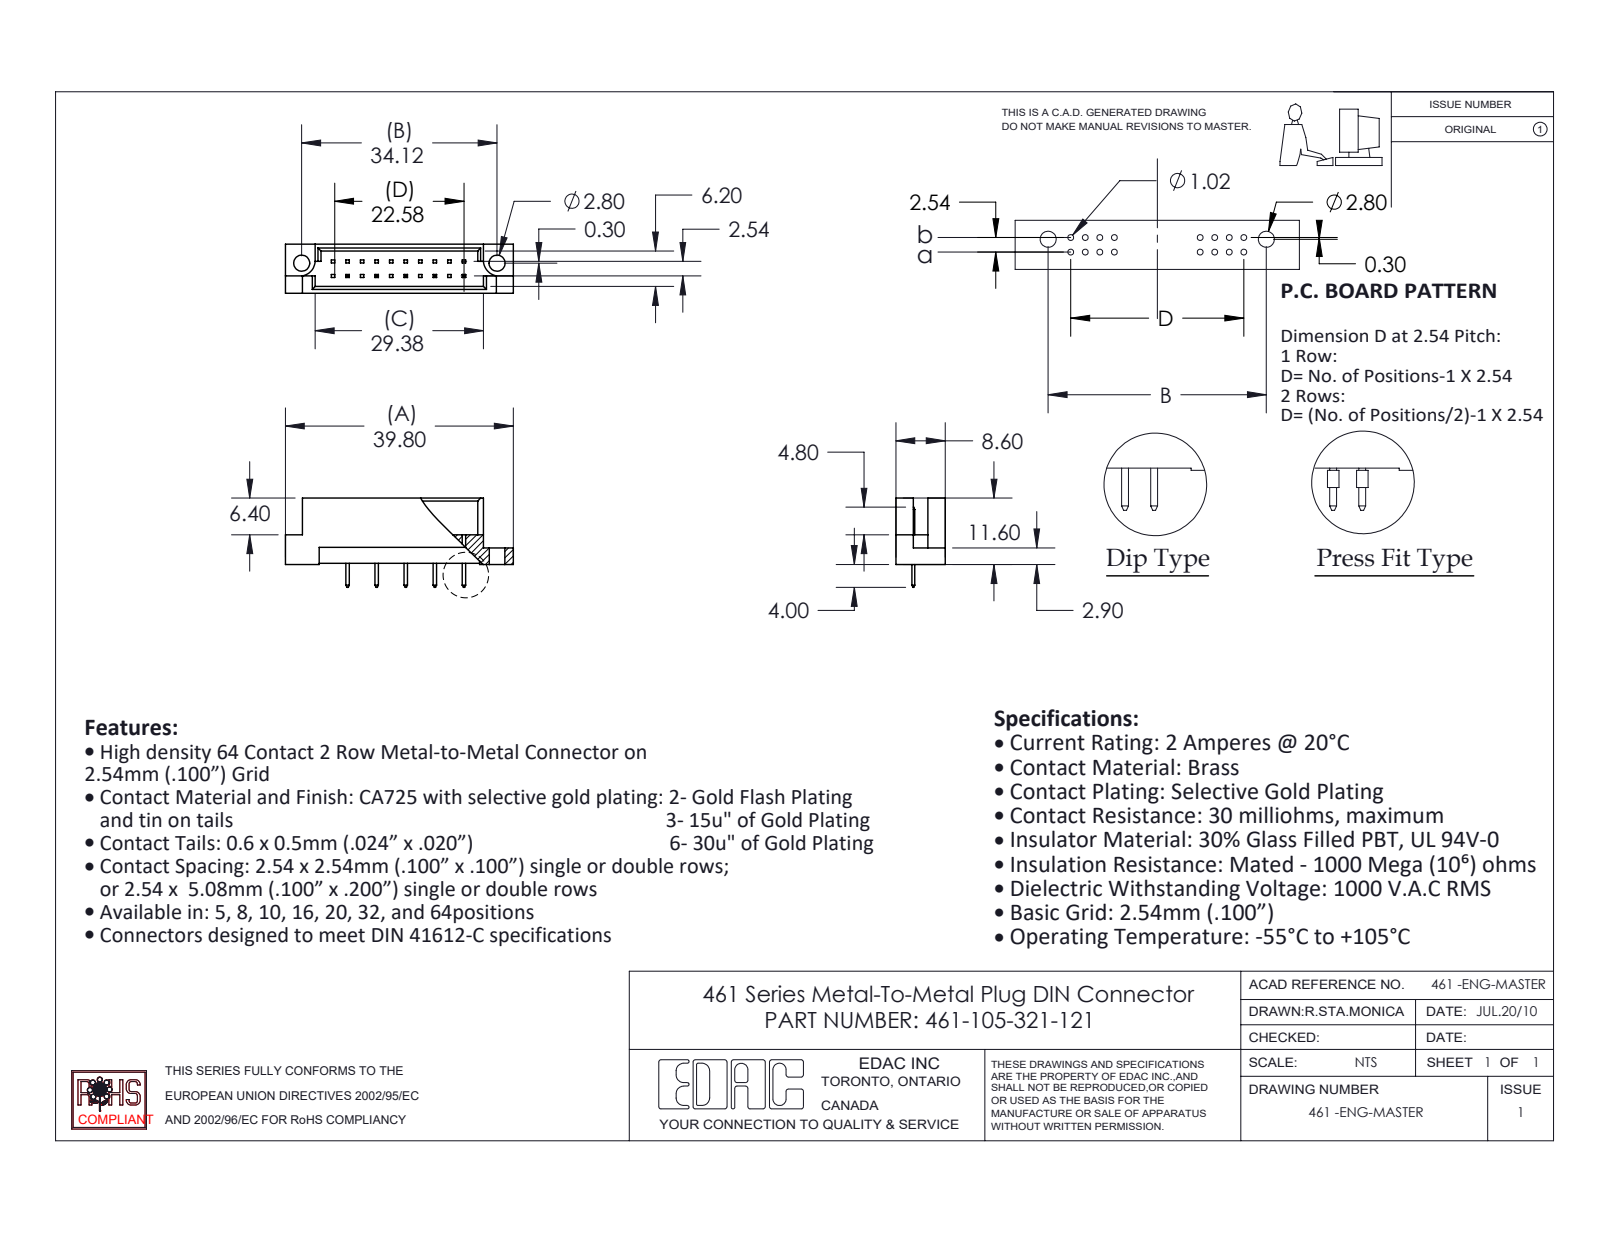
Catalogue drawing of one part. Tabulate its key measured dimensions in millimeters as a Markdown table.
| quantity | value |
| --- | --- |
| part name | 461-105-321-121; 461 Part_20; 461-290_21 |
| STEP written by | SolidWorks 2020 (CONFIG_CONTROL_DESIGN) |
| units | millimeters |
| bodies | 6 solids, 198 faces (192 planar, 6 cylindrical, 0 other) |
| overall size | 39.8 × 15.6 × 8.6 |
| volume | 1 925 mm³ |
| surface area | 2 490 mm² |
| round holes (diameter × count) | 2.8 × 2 |
| partial cylindrical surfaces (radius × count) | 2.8 × 2 |
| main face-to-face distances | 1.2, 7.4, 8.6, 6.2, 5, 3.28, 5.32, 2.08, 4.12, 2.78 |
| hole center spacings | 34.12 |
